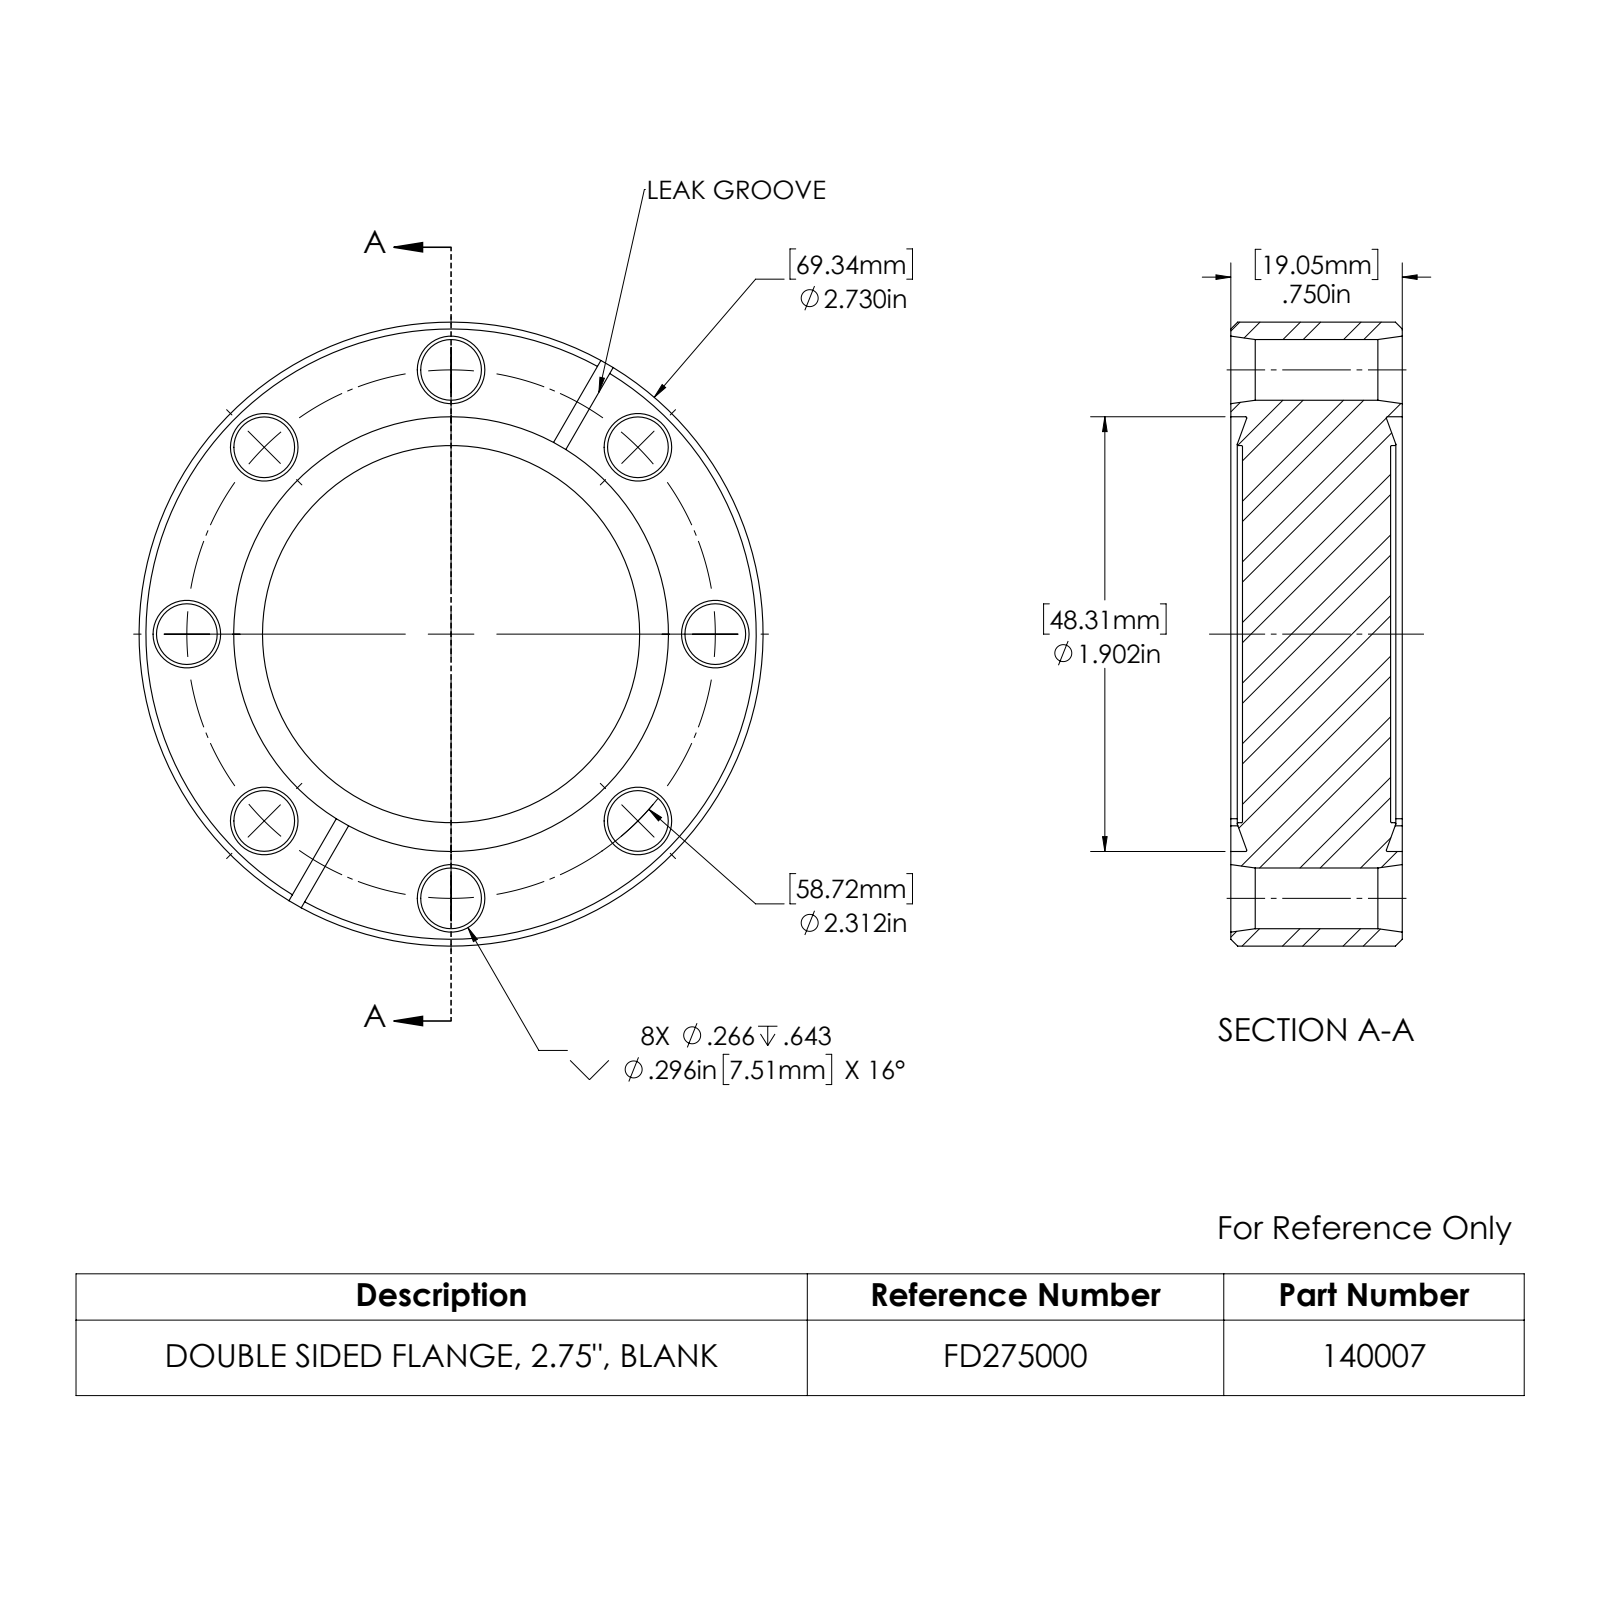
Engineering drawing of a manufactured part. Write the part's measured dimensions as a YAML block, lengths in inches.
part_name: "140007_A"
step_written_by: "SolidWorks 2022 (CONFIG_CONTROL_DESIGN)"
units: inches
bodies: {solids: 1, faces: 98, planar: 14, cylindrical: 30, other: 54}
overall_size: [2.73, 2.73, 0.75]
volume: 3.74
surface_area: 23.24
round_holes:
  - {diameter: 0.266, count: 8}
  - {diameter: 1.65, count: 1}
  - {diameter: 1.902, count: 1}
round_bosses_or_shafts:
  - {diameter: 2.73, count: 1}
partial_cylinders:
  - {radius: 1.25, count: 4}
face_to_face_distances: [0.051, 0.699, 0.75, 0.648, 0.062]
hole_center_spacings: [0.885, 1.156, 1.635, 2.136, 2.312]
